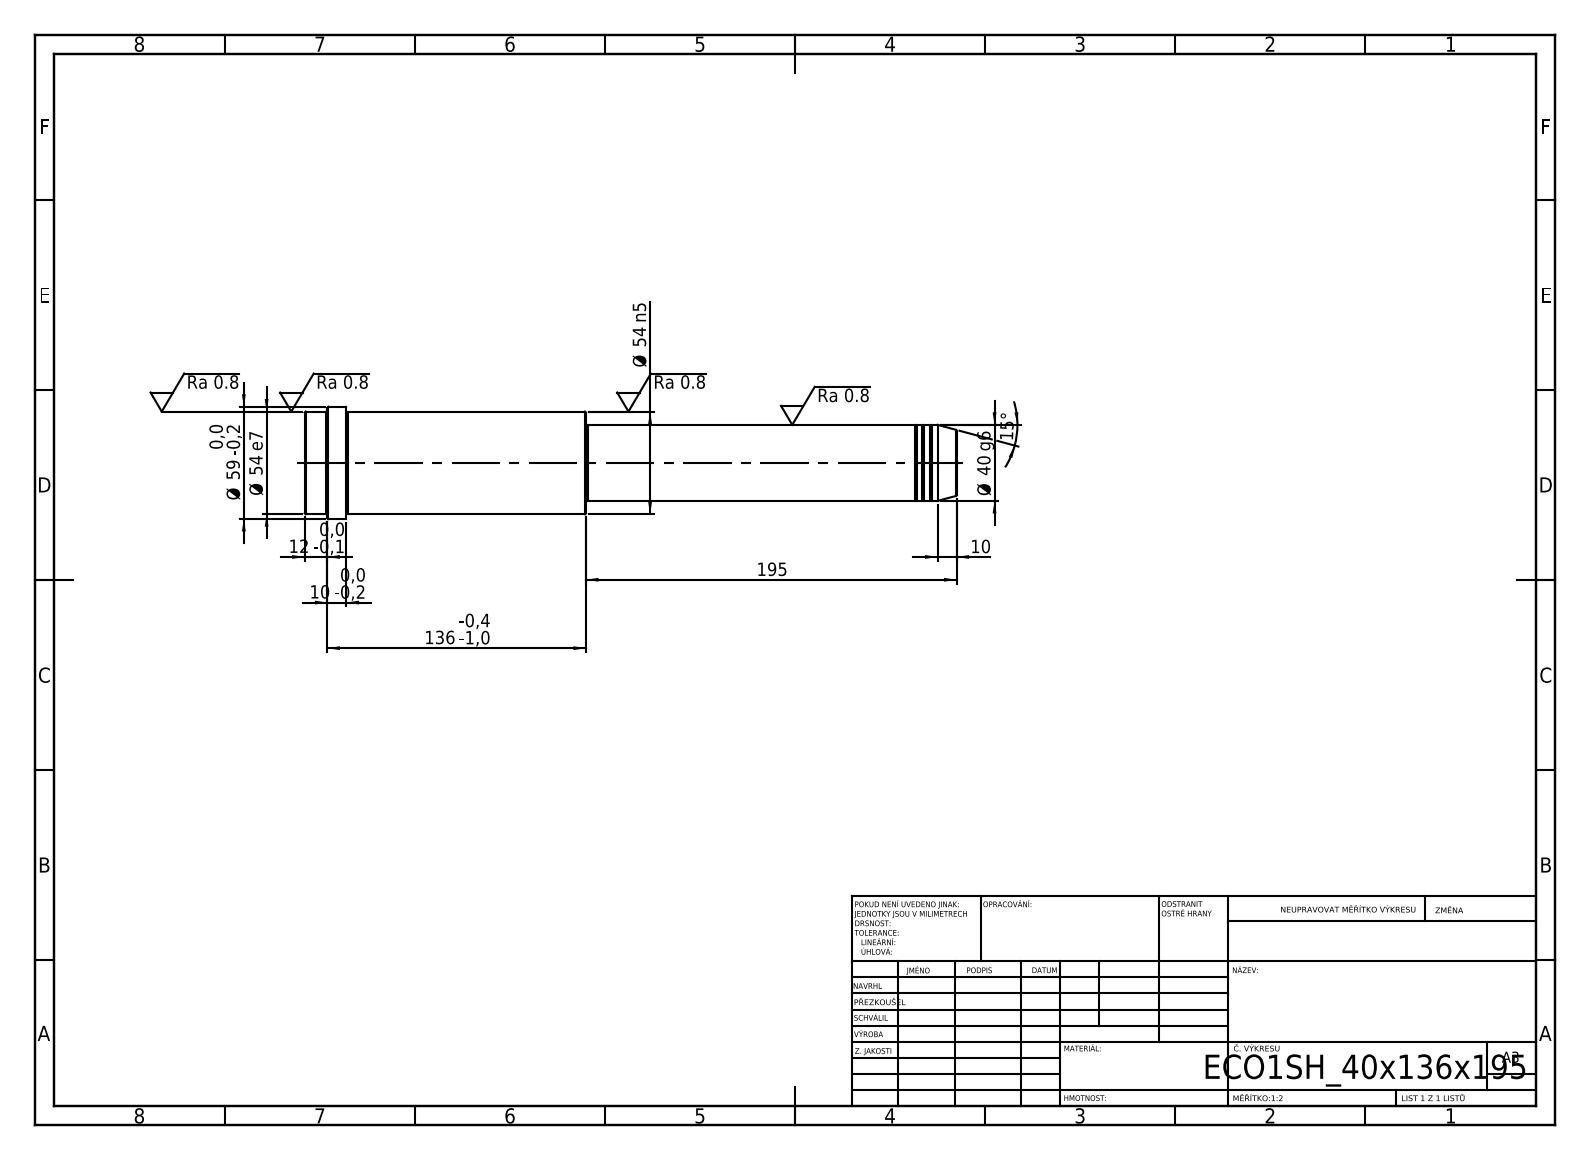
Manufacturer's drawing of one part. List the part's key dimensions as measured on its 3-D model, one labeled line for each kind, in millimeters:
STEP written by: SolidWorks 2019 (CONFIG_CONTROL_DESIGN)
Units: millimetres
Bodies: 1 solid, 52 faces (6 planar, 16 cylindrical, 30 other)
Overall size (bounding box): 343 × 59 × 59
Volume: 586 417 mm³ · Surface area: 55 227 mm²
Round bosses / shafts (diameter × count): ⌀59 ×1, ⌀54 ×1, ⌀40 ×1, ⌀39 ×1
Main face-to-face distances: 148, 195, 343, 321, 126, 22, 331, 136, 10, 12
